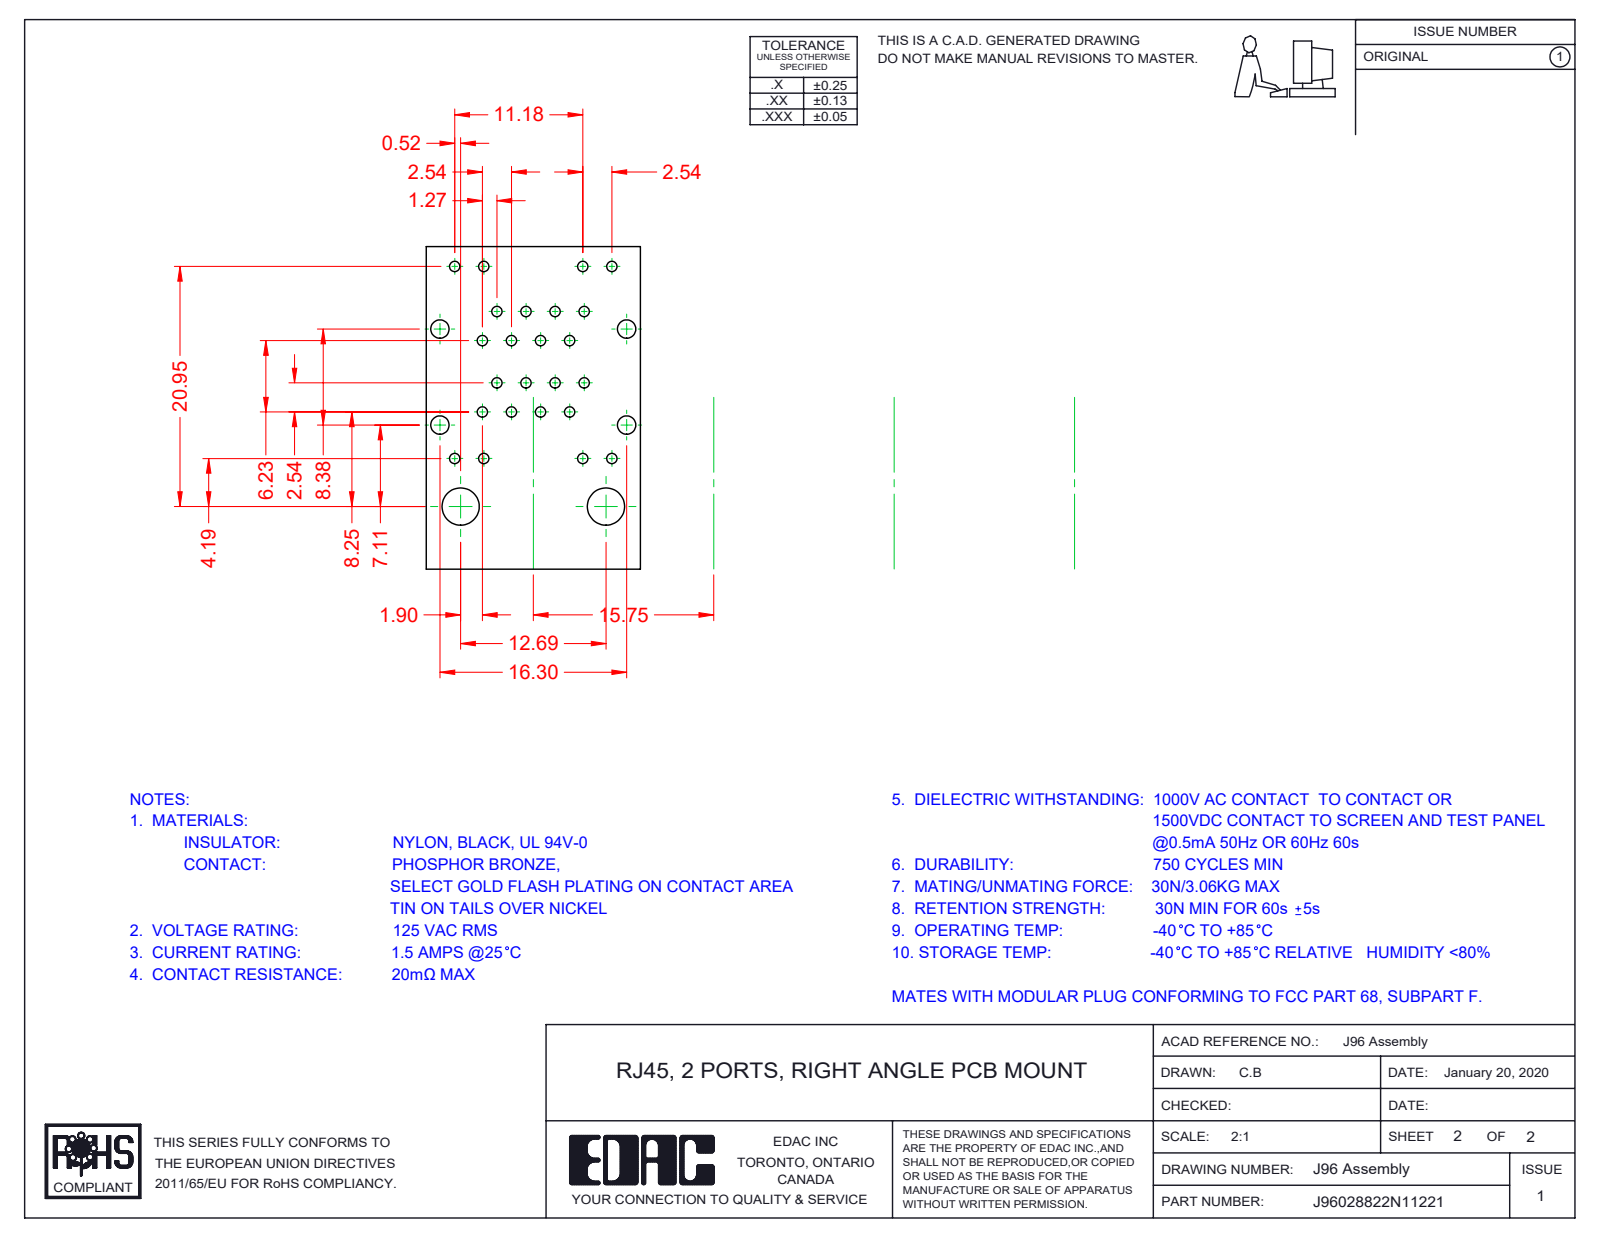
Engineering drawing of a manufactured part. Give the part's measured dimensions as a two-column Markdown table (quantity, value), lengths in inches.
| quantity | value |
| --- | --- |
| part name | 96 Contact Lock Upper; 96 LED RH Lower_1-Yellow; 96 LED LH Upper_1-Yellow; 96 Shield_2 Ports LED - EMI (+8 more) |
| STEP written by | SolidWorks 2016 (CONFIG_CONTROL_DESIGN) |
| units | inches |
| bodies | 27 solids, 2417 faces (1865 planar, 446 cylindrical, 106 other) |
| overall size | 1.235 × 1.129 × 0.661 |
| volume | 0.418 in³ |
| surface area | 29.6 in² |
| partial cylindrical surfaces (radius × count) | 0.01 × 48, 0.006 × 32, 0.014 × 24, 0.02 × 16, 0.039 × 16, 0.008 × 14, 0.028 × 9, 0.079 × 5 |
| main face-to-face distances | 0.642, 0.634, 0.069, 0.65, 0.581, 0.061, 0.573, 0.021, 0.058, 0.441 |
